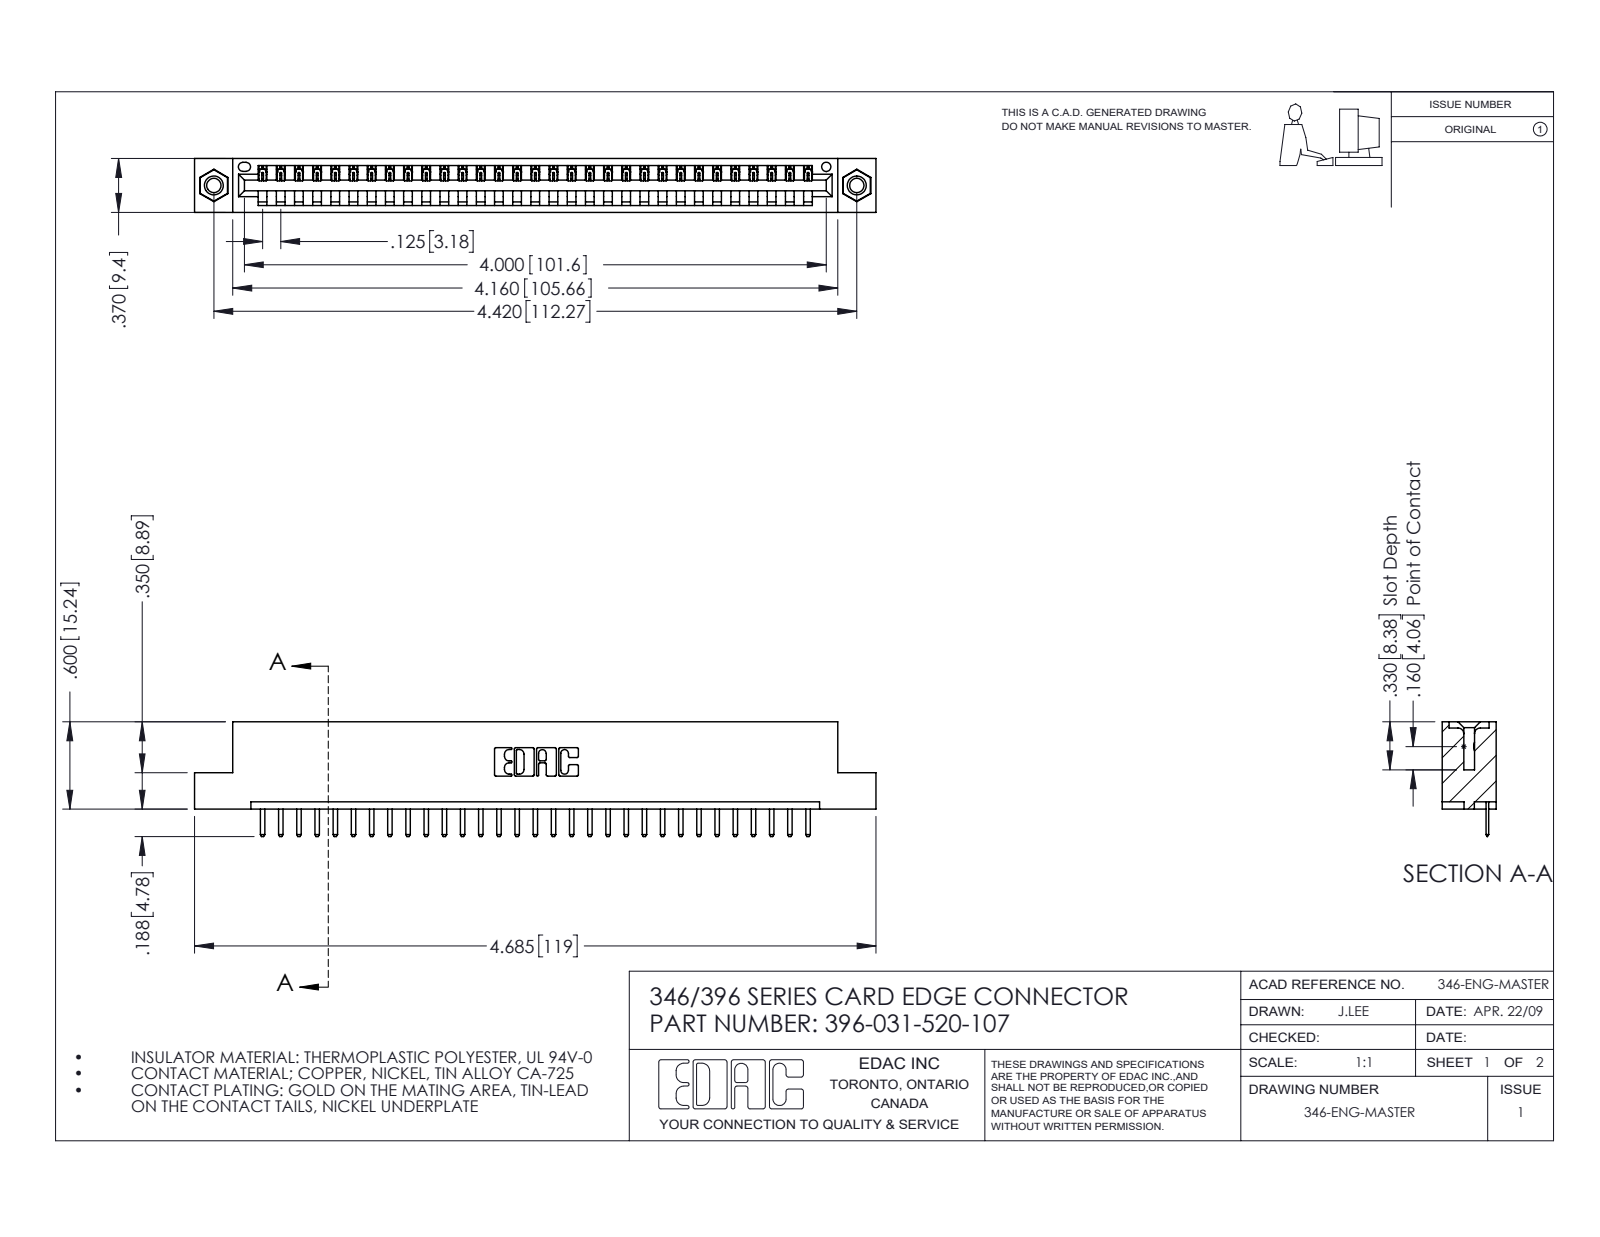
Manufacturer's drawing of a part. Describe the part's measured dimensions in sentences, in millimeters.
The part is named "396-031-520-107; 346 Part_Flush Mounting Lugs - 0.156 Dia-TI; 345-250-001_345-250-005-103; 345-292-001_345-293-120". Its 3-D file was written by "SolidWorks 2016 (CONFIG_CONTROL_DESIGN)". It is 34 solids with 2104 faces: 1410 planar, 678 cylindrical and 16 other. Overall it measures 119 by 20 by 9.4 millimeters. Its volume is 11 200 cubic millimeters and its surface area 13 630 square millimeters. Round holes: 2 of diameter 2.5, 2 of diameter 3.2, 2 of diameter 4, 1 of diameter 1.6. Round bosses or shafts: 2 of diameter 3.9. Partial cylindrical surfaces (rounded edges, fillets, slot ends): 64 of radius 0.3, 62 of radius 0.2, 22 of radius 0.3, 6 of radius 0.2, 6 of radius 0.8, 3 of radius 0.7, 2 of radius 0.8, 2 of radius 1. The main face-to-face distances are 1.2, 8.2, 9.4, 6.4, 3.8, 5.6, 2.5, 4.4, 1.8, 7.6. The hole center spacings are 6.2, 107, 112.3.
